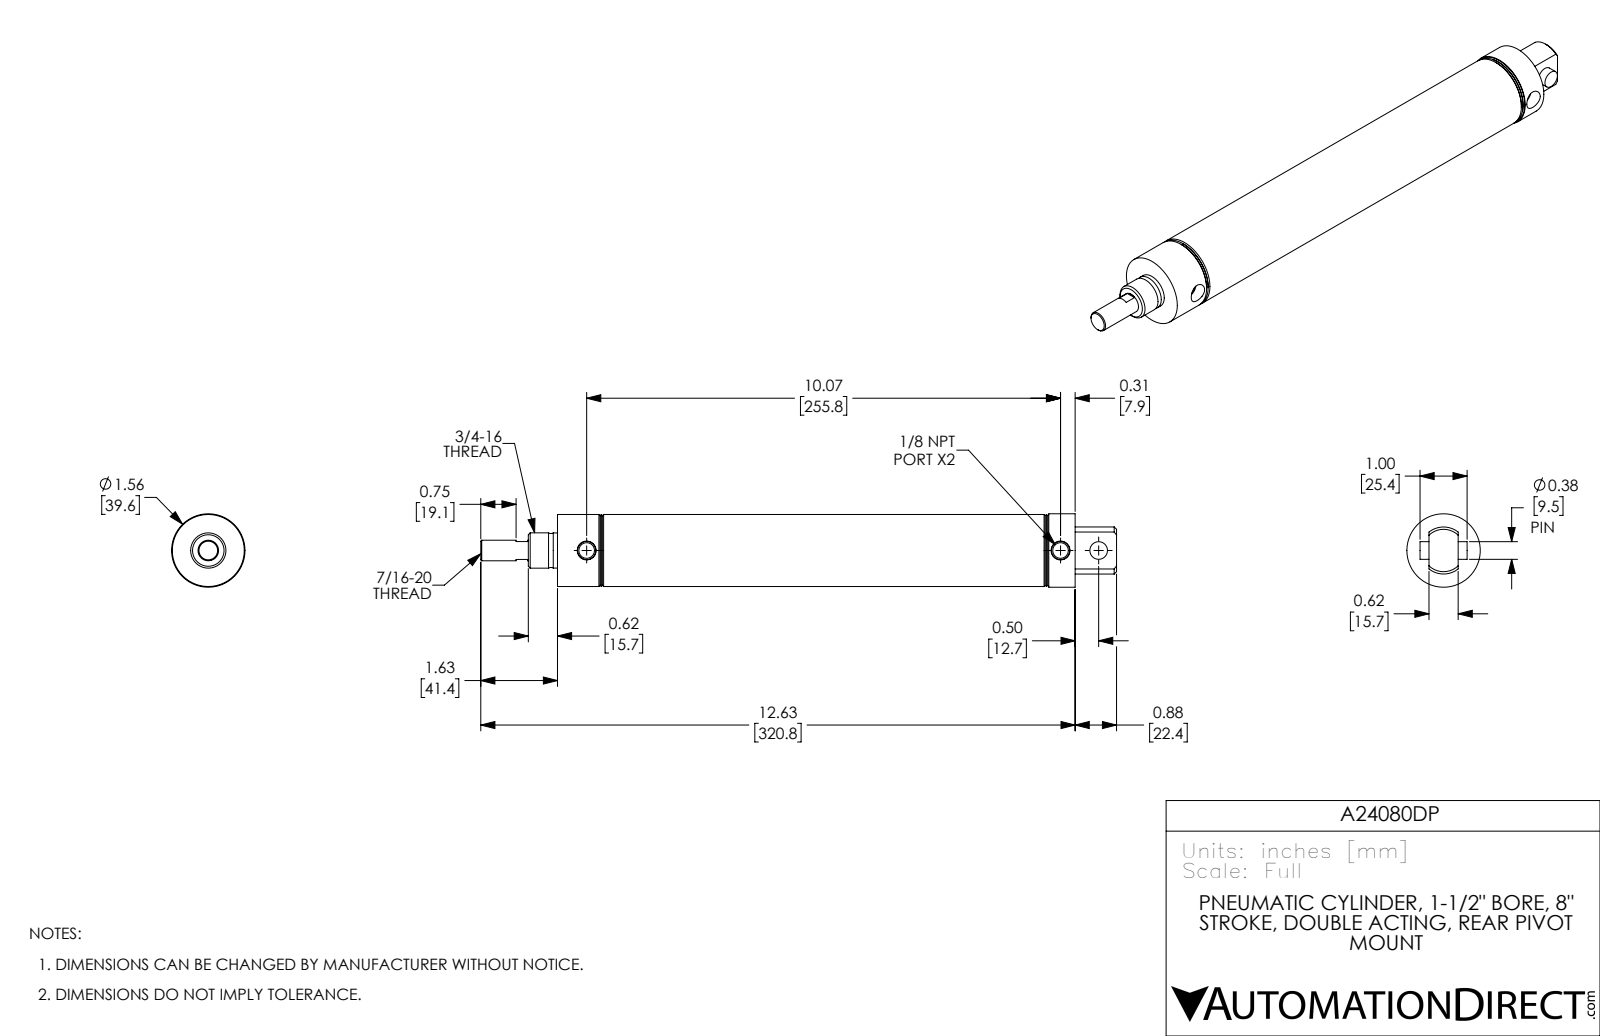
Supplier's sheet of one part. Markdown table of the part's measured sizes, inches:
| quantity | value |
| --- | --- |
| part name | A24080DP-Pin; A24080DP; A24080DP-MainBody; A24080DP-Rod |
| STEP written by | SolidWorks 2017 (AUTOMOTIVE_DESIGN) |
| units | inches |
| bodies | 3 solids, 84 faces (22 planar, 28 cylindrical, 34 other) |
| overall size | 13.51 × 1.56 × 1.56 |
| volume | 8.18 in³ |
| surface area | 130.6 in² |
| round holes (diameter × count) | 0.332 × 2, 0.375 × 1, 0.437 × 1, 1.5 × 1 |
| round bosses / shafts (diameter × count) | 1.56 × 1, 1.53 × 1, 0.75 × 1, 0.746 × 1 |
| partial cylindrical surfaces (radius × count) | 0.5 × 1 |
| main face-to-face distances | 1.25, 9.75, 0.5, 8.5, 8, 9.25, 1.75, 11, 0.62, 0.88 |
| hole center spacings | 0.81, 10.07, 10.88 |
